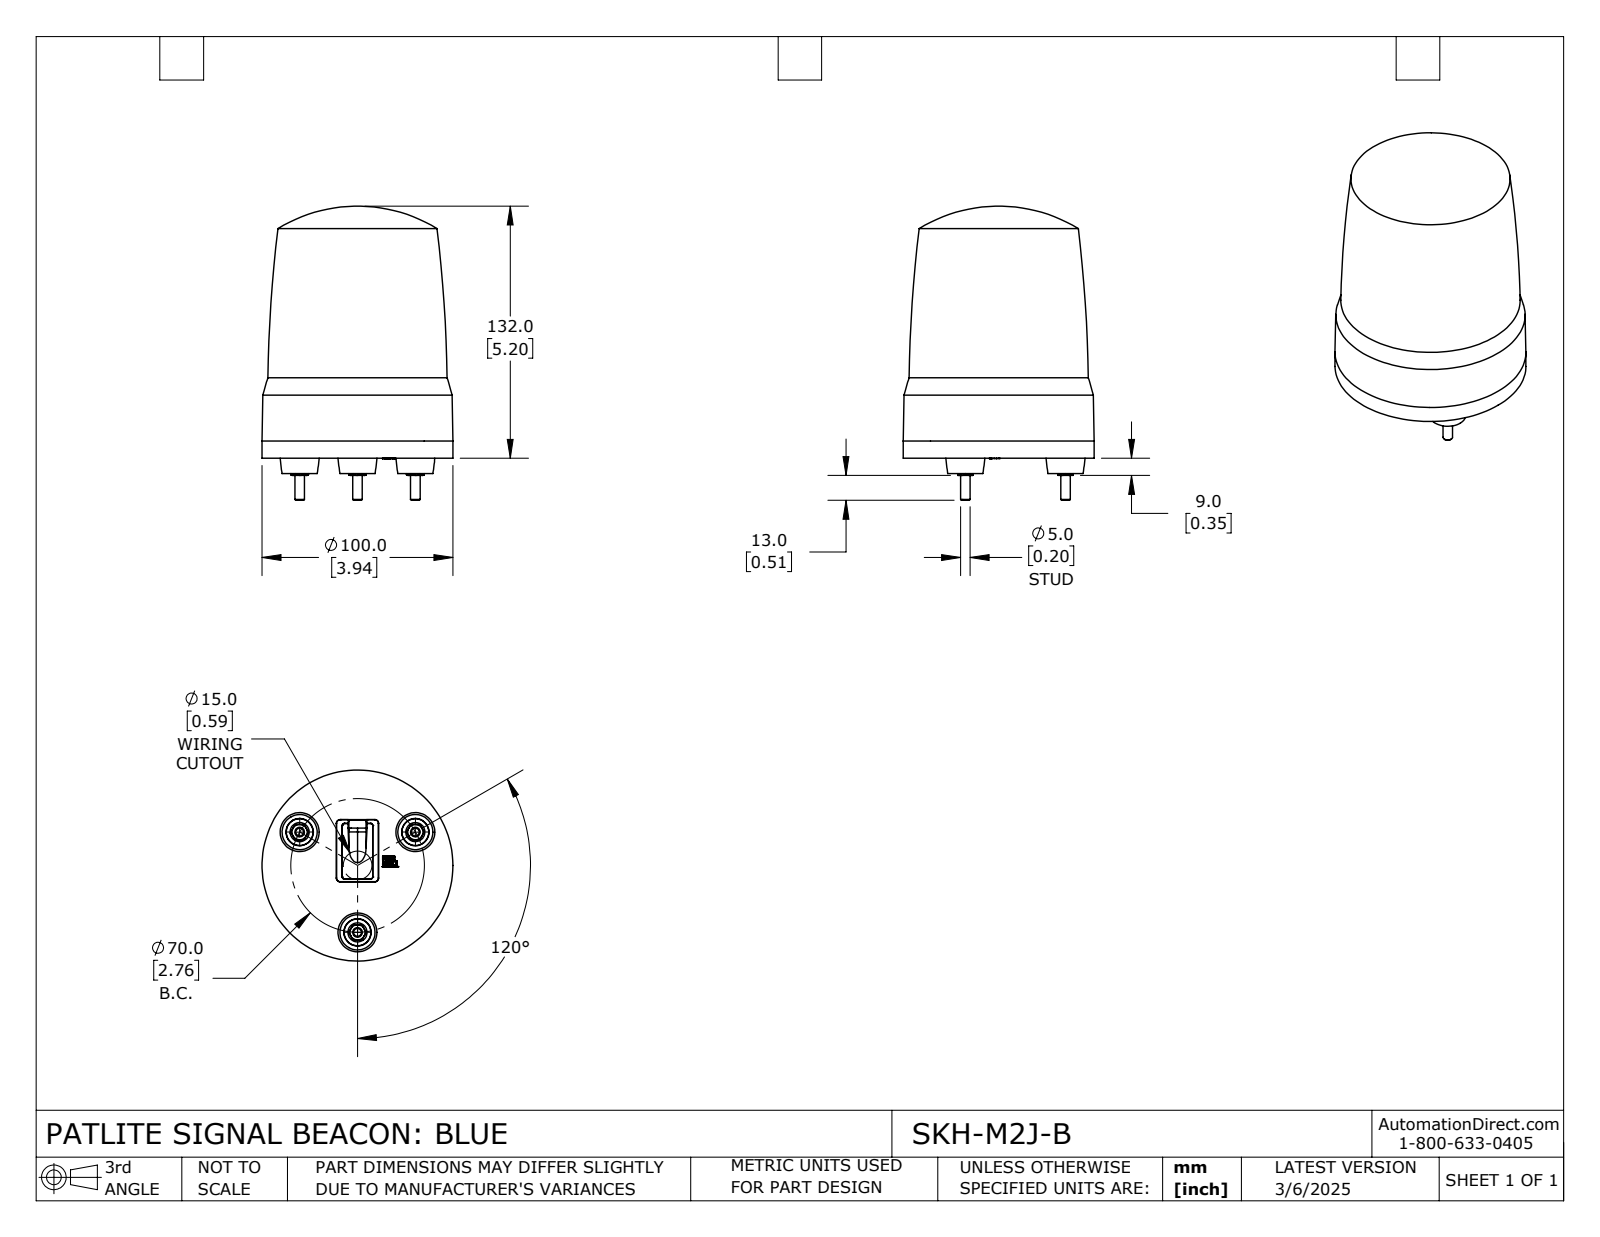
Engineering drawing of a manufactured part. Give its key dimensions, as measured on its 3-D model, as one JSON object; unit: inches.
{"part_name": "SKH-M2J-B", "step_written_by": "SolidWorks 2024 (CONFIG_CONTROL_DESIGN)", "units": "inches", "bodies": {"solids": 1, "faces": 327, "planar": 159, "cylindrical": 14, "other": 154}, "overall_size": [6.063, 3.937, 3.937], "volume_in3": 52.48, "surface_area_in2": 81.51, "round_bosses_or_shafts": [[0.394, 3], [0.197, 3], [3.937, 1]], "face_to_face_distances": [0.315, 0.033, 0.348, 0.063, 0.411, 0.096, 0.15, 0.165, 0.199, 0.262]}
